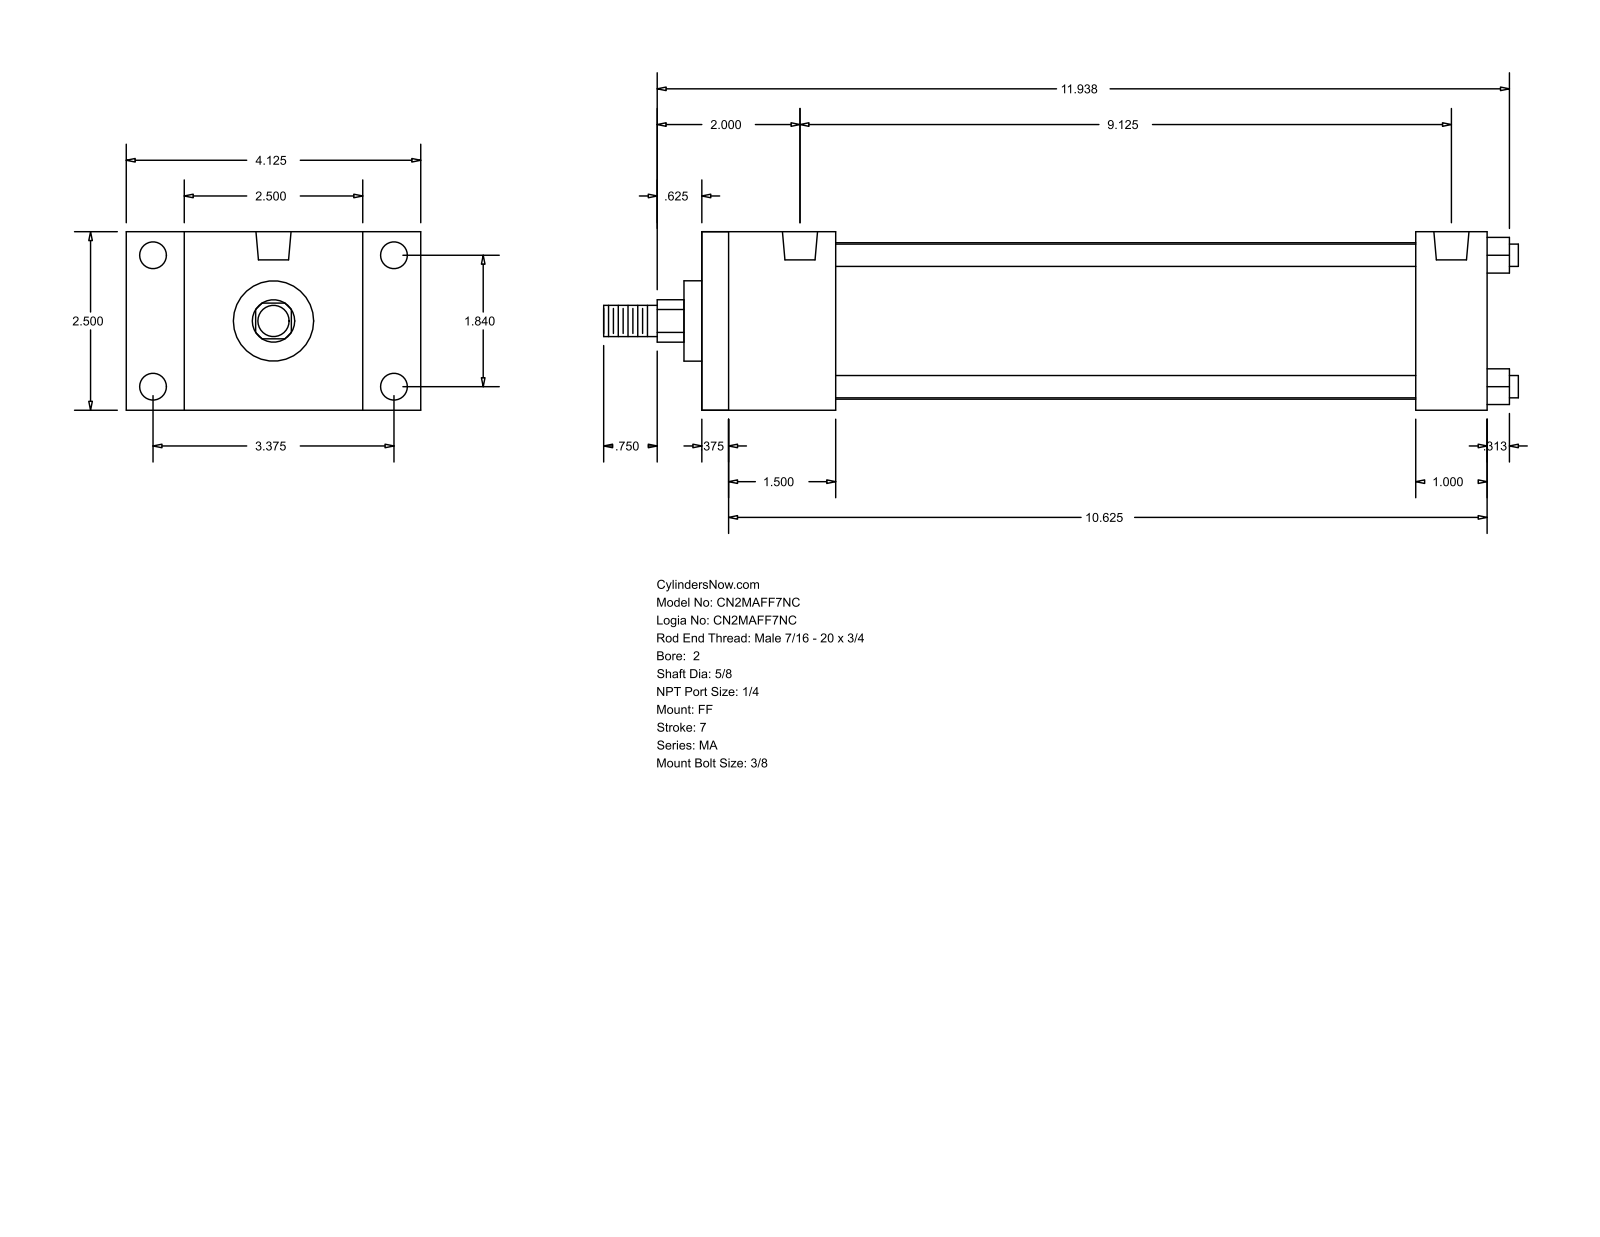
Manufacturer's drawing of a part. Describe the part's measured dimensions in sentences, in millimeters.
The part is named "MA_FF__0200_0.625". Its 3-D file was written by "GSSL Pune (CONFIG_CONTROL_DESIGN)". It is 0 solids with 92 faces: 64 planar, 28 cylindrical and 0 other. Overall it measures 325.44 by 104.78 by 63.5 millimeters. Round holes: 4 of diameter 7.94, 4 of diameter 9.53, 2 of diameter 12.49. Round bosses or shafts: 4 of diameter 7.94, 1 of diameter 55.63, 1 of diameter 28.57, 1 of diameter 15.88, 1 of diameter 11.11. Partial cylindrical surfaces (rounded edges, fillets, slot ends): 1 of radius 7.54. The main face-to-face distances are 63.5, 279.39, 9.52, 269.87, 38.1, 47.62, 254, 244.48, 206.38, 231.77. The hole center spacings are 46.74, 85.72, 97.63, 231.77.
